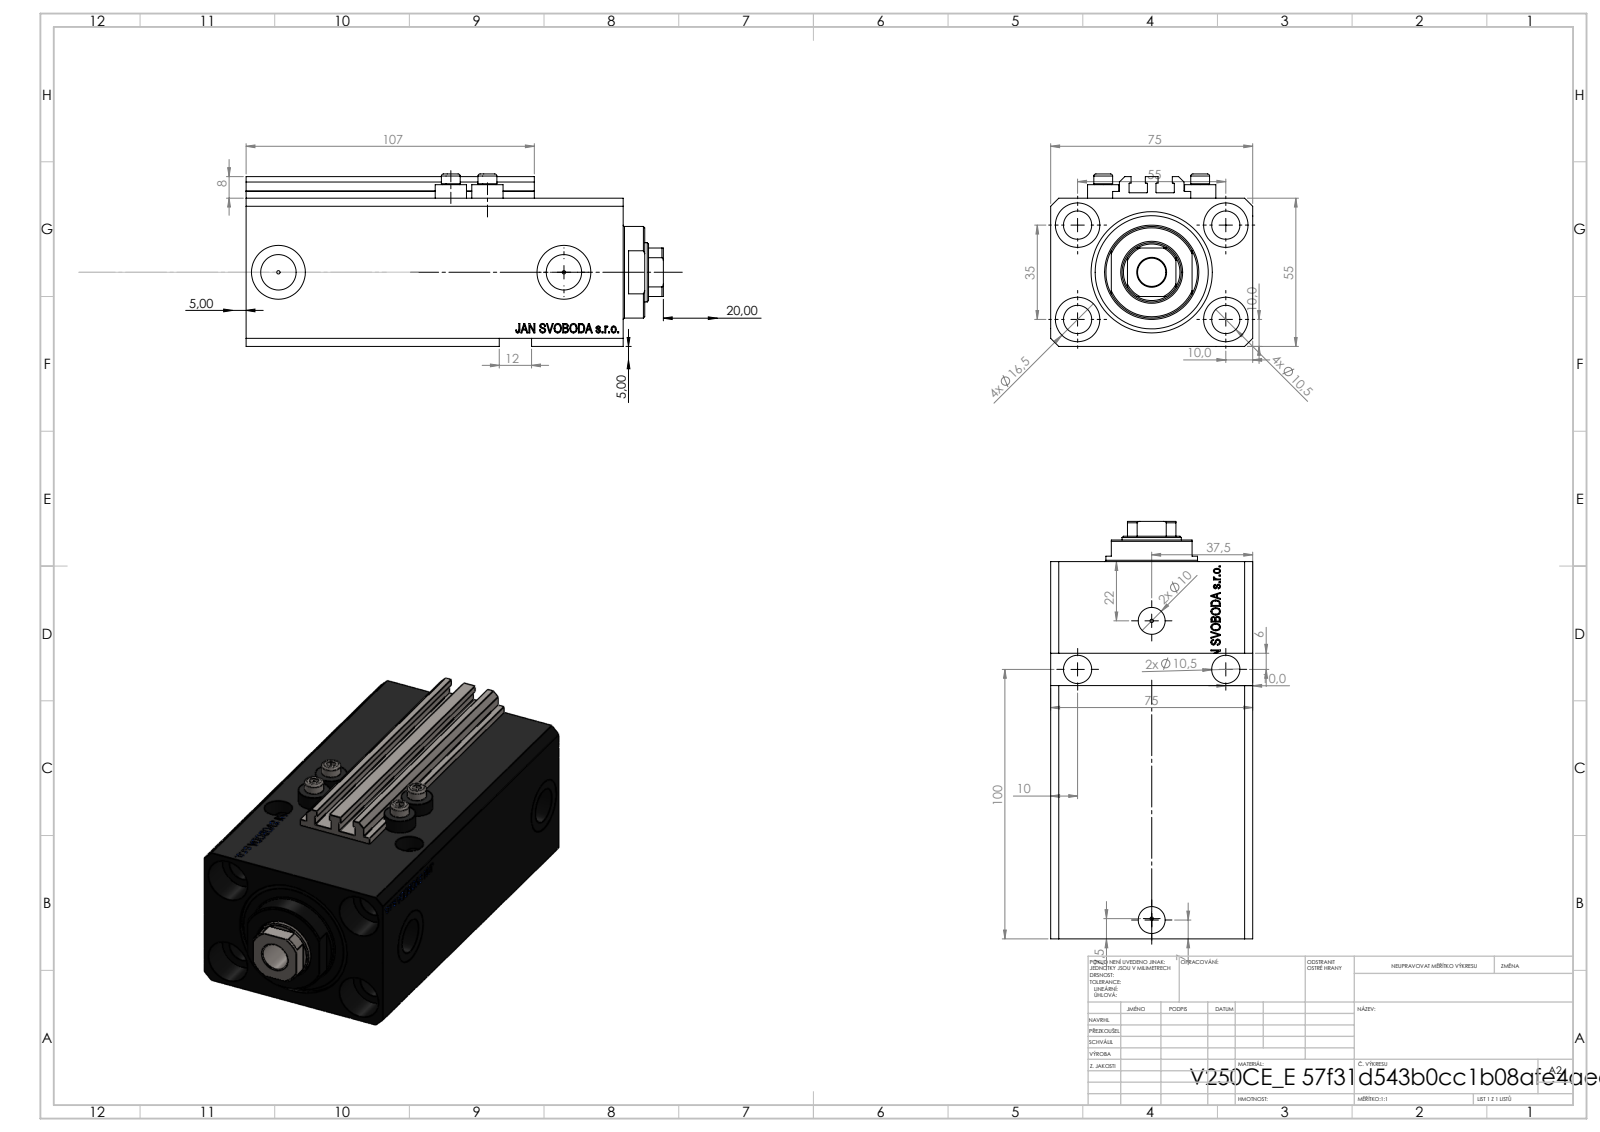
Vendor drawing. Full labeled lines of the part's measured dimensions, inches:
Part name (STEP PRODUCT): V250CE_VC_E; ALLEN BOLT V250CE; V250CE_C_VCP; V250CE_E_Body
STEP written by: SolidWorks 2019 (CONFIG_CONTROL_DESIGN)
Units: inches
Bodies: 8 solids, 1100 faces (518 planar, 158 cylindrical, 424 other)
Overall size (bounding box): 6.102 × 2.953 × 2.52
Volume: 29.39 in³ · Surface area: 180.5 in²
Round holes (diameter × count): ⌀0.413 ×9, ⌀0.049 ×4, ⌀0.157 ×4, ⌀0.65 ×4, ⌀0.394 ×2, ⌀0.518 ×2, ⌀0.787 ×2, ⌀0.866 ×1, ⌀1.26 ×1, ⌀1.772 ×1
Round bosses / shafts (diameter × count): ⌀0.457 ×4, ⌀0.276 ×4, ⌀1.339 ×1
Partial cylindrical surfaces — rounded edges, fillets, slot ends (radius × count): R0.008 ×10, R0.413 ×1
Main face-to-face distances: 2.165, 2.953, 0.591, 0.39, 5.512, 4.921, 0.118, 2.244, 4.531, 5.122
Hole centre spacings: 1.283, 1.294, 2.165, 3.818, 0.535, 0.555, 1.016, 1.283
